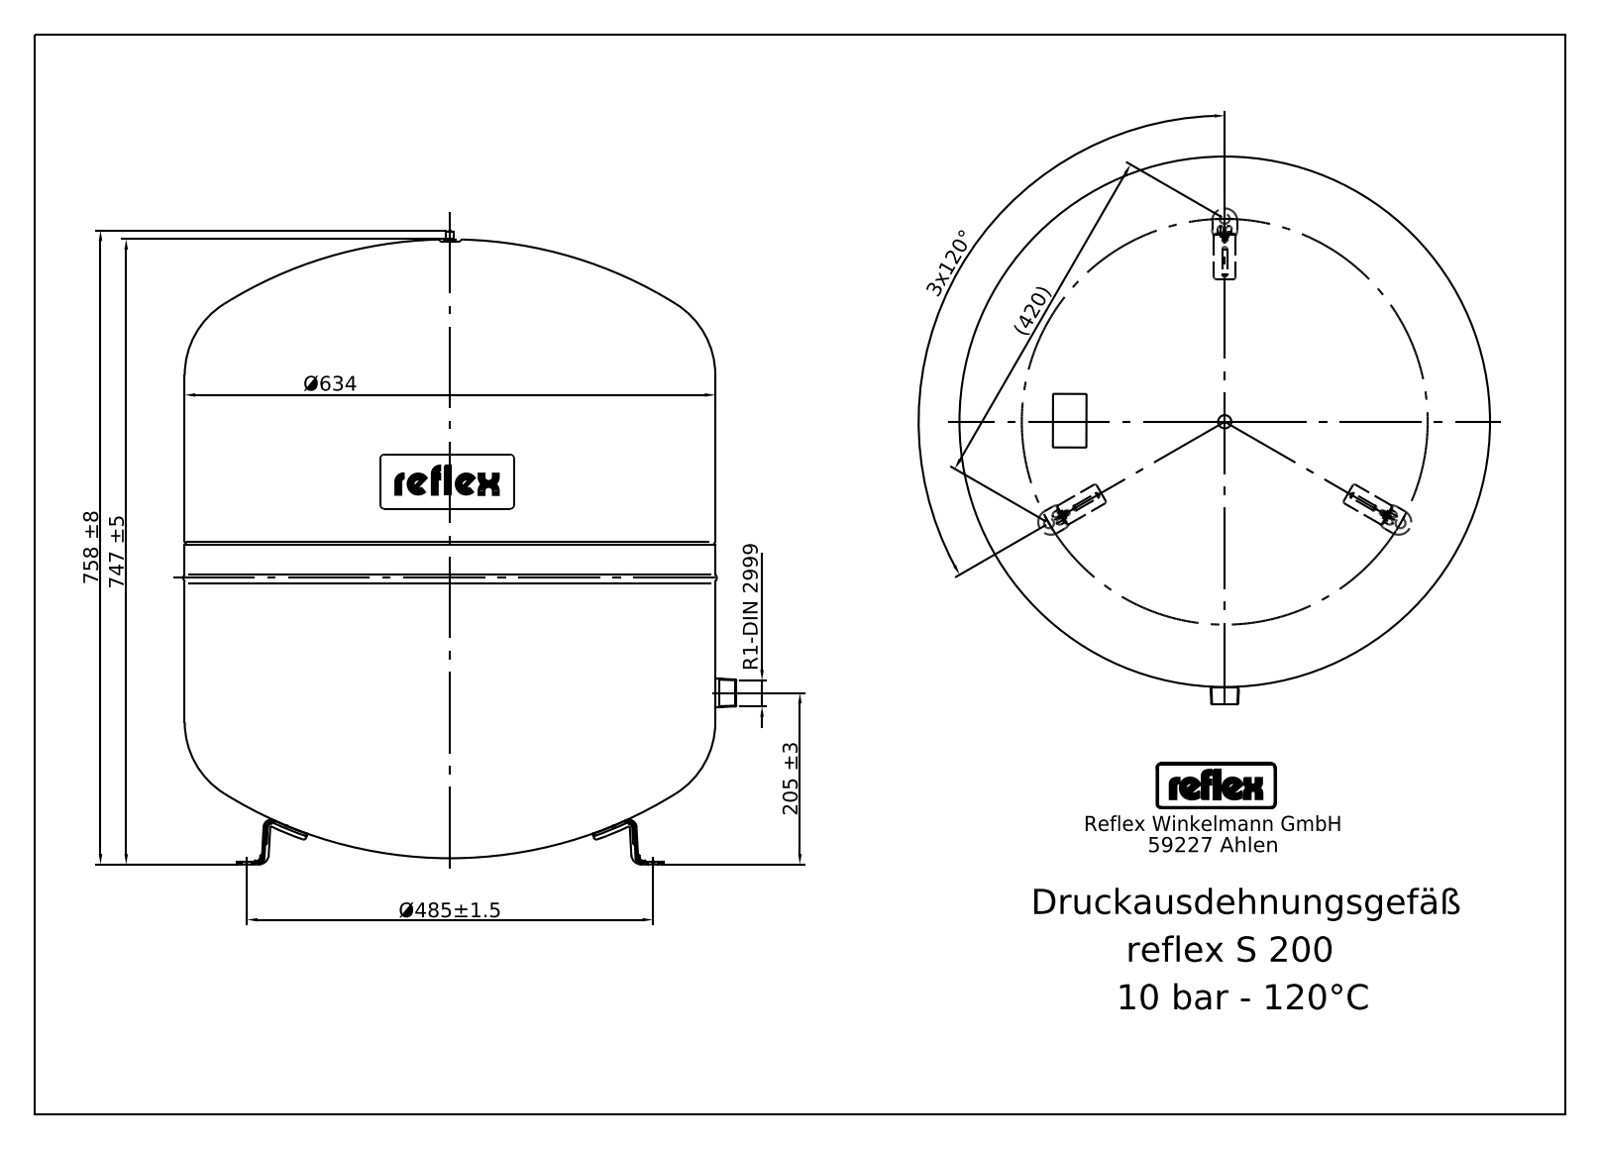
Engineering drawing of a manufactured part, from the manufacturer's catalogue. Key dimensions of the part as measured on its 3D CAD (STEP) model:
STEP written by: Mechanical Desktop 2011 (CONFIG_CONTROL_DESIGN)
Units: millimetres
Bodies: 16 solids, 208 faces (79 planar, 76 cylindrical, 53 other)
Overall size (bounding box): 759.5 × 663.4 × 642.8
Volume: 198 600 000 mm³ · Surface area: 3 025 000 mm²
Round holes (diameter × count): ⌀15 ×3, ⌀5.64 ×1
Round bosses / shafts (diameter × count): ⌀634 ×1, ⌀33.7 ×1, ⌀6.84 ×1, ⌀3.6 ×1, ⌀2.4 ×1
Partial cylindrical surfaces — rounded edges, fillets, slot ends (radius × count): R148.38 ×9, R150.38 ×9, R15 ×6, R3.94 ×4, R1.57 ×3, R2.69 ×2, R4.72 ×2, R6.49 ×2
Main face-to-face distances: 416, 208, 3.15, 168, 376, 584, 2, 170, 378, 586
Hole centre spacings: 242.5, 420.02
